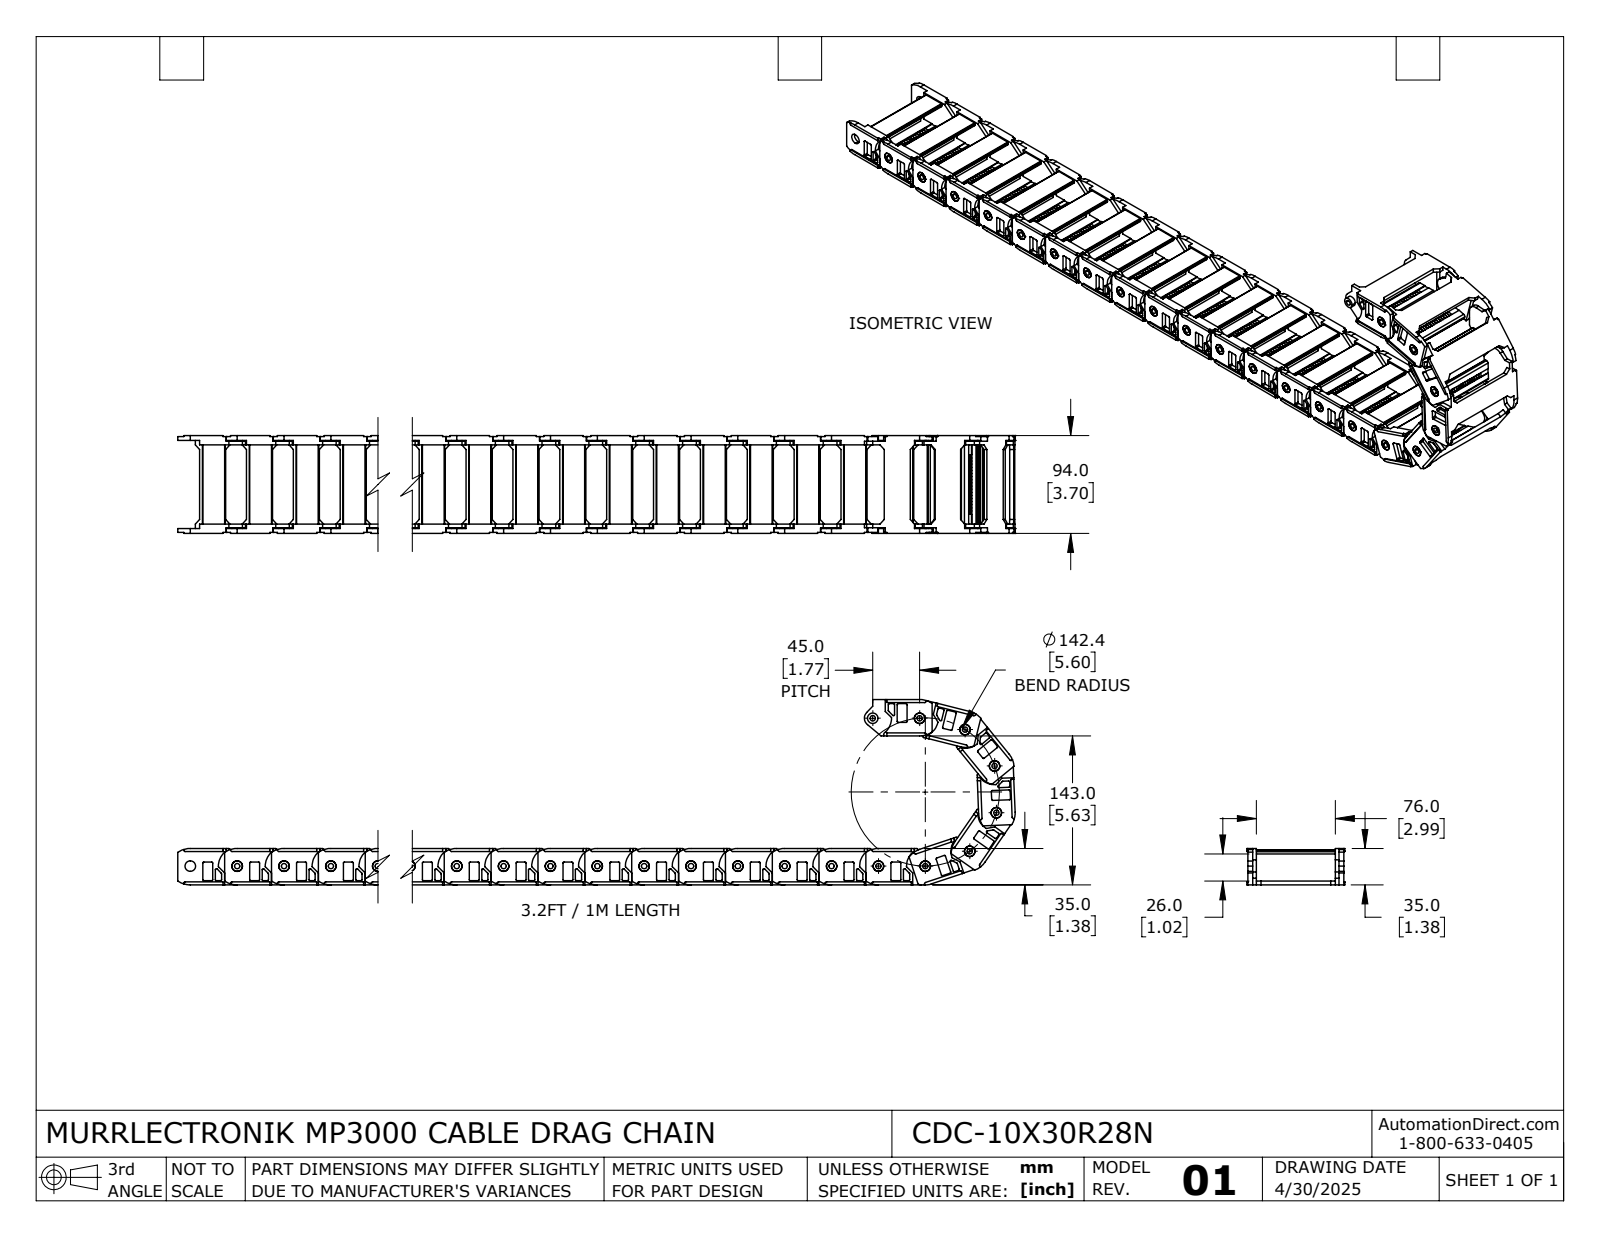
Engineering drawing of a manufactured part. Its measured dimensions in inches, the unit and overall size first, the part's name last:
Units: inches
Overall size (bounding box): 32.216 × 7.013 × 3.701
Round holes (diameter × count): ⌀0.201 ×22, ⌀0.398 ×22
Round bosses / shafts (diameter × count): ⌀0.394 ×22
Partial cylindrical surfaces — rounded edges, fillets, slot ends (radius × count): R0.039 ×176, R0.02 ×88, R0.059 ×44, R0.079 ×44, R0.827 ×44, R0.11 ×22, R0.315 ×22, R0.709 ×22
Main face-to-face distances: 3.307, 0.315, 0.157, 0.15, 1.181, 1.331, 0.146, 3.476, 0.169, 3.161
Hole centre spacings: 1.772, 3.543, 5.315, 7.087, 8.858, 10.63, 12.402, 14.173
Volume: 44.66 in³ · Surface area: 695.2 in²
Bodies: 22 solids, 4752 faces (3652 planar, 1100 cylindrical, 0 other)
Part name (STEP PRODUCT): CDC-10X30R28N
STEP written by: SolidWorks 2024 (AUTOMOTIVE_DESIGN)
